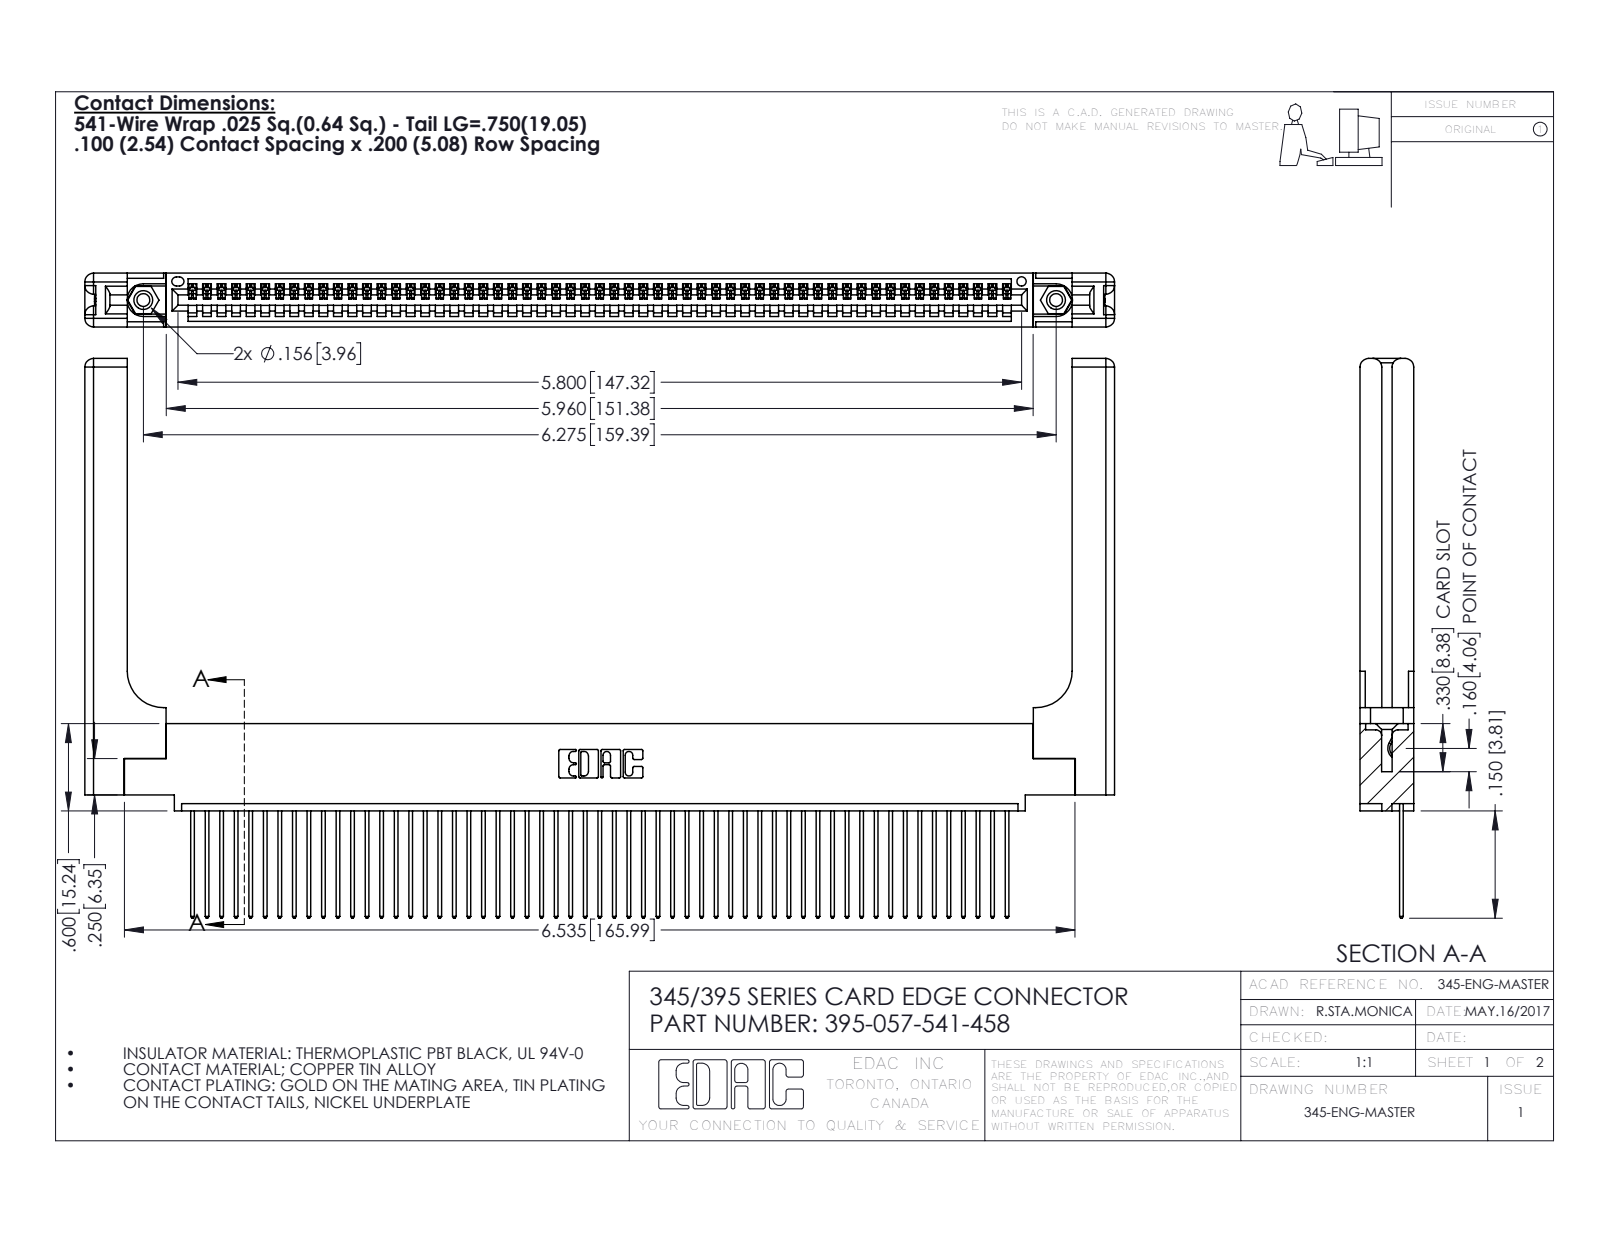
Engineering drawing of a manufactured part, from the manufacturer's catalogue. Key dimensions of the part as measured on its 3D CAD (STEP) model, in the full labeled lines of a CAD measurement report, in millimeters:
Part name (STEP PRODUCT): 345-220-058_345-220-058; 345-292-001_345-293-141; 345 Part_0.110 Offset - 0.156 Dia-TH; 345-250-001_345-250-001-102 (+1 more)
STEP written by: SolidWorks 2016 (CONFIG_CONTROL_DESIGN)
Units: millimetres
Bodies: 62 solids, 3692 faces (2512 planar, 1120 cylindrical, 60 other)
Overall size (bounding box): 179.8 × 97.7 × 9.4
Volume: 25 830 mm³ · Surface area: 29 710 mm²
Round holes (diameter × count): ⌀2.3 ×2, ⌀3.2 ×2, ⌀4 ×2, ⌀1.6 ×1
Round bosses / shafts (diameter × count): ⌀3.9 ×2
Partial cylindrical surfaces — rounded edges, fillets, slot ends (radius × count): R0.2 ×114, R0.3 ×114, R0.3 ×22, R1.5 ×16, R0.2 ×6, R0.8 ×6, R0.7 ×3, R0.8 ×2
Main face-to-face distances: 1.8, 7.6, 9.4, 2.5, 6.9, 0.6, 5.1, 5.7, 3.8, 3.8
Hole centre spacings: 6.9, 153.4, 159.4
